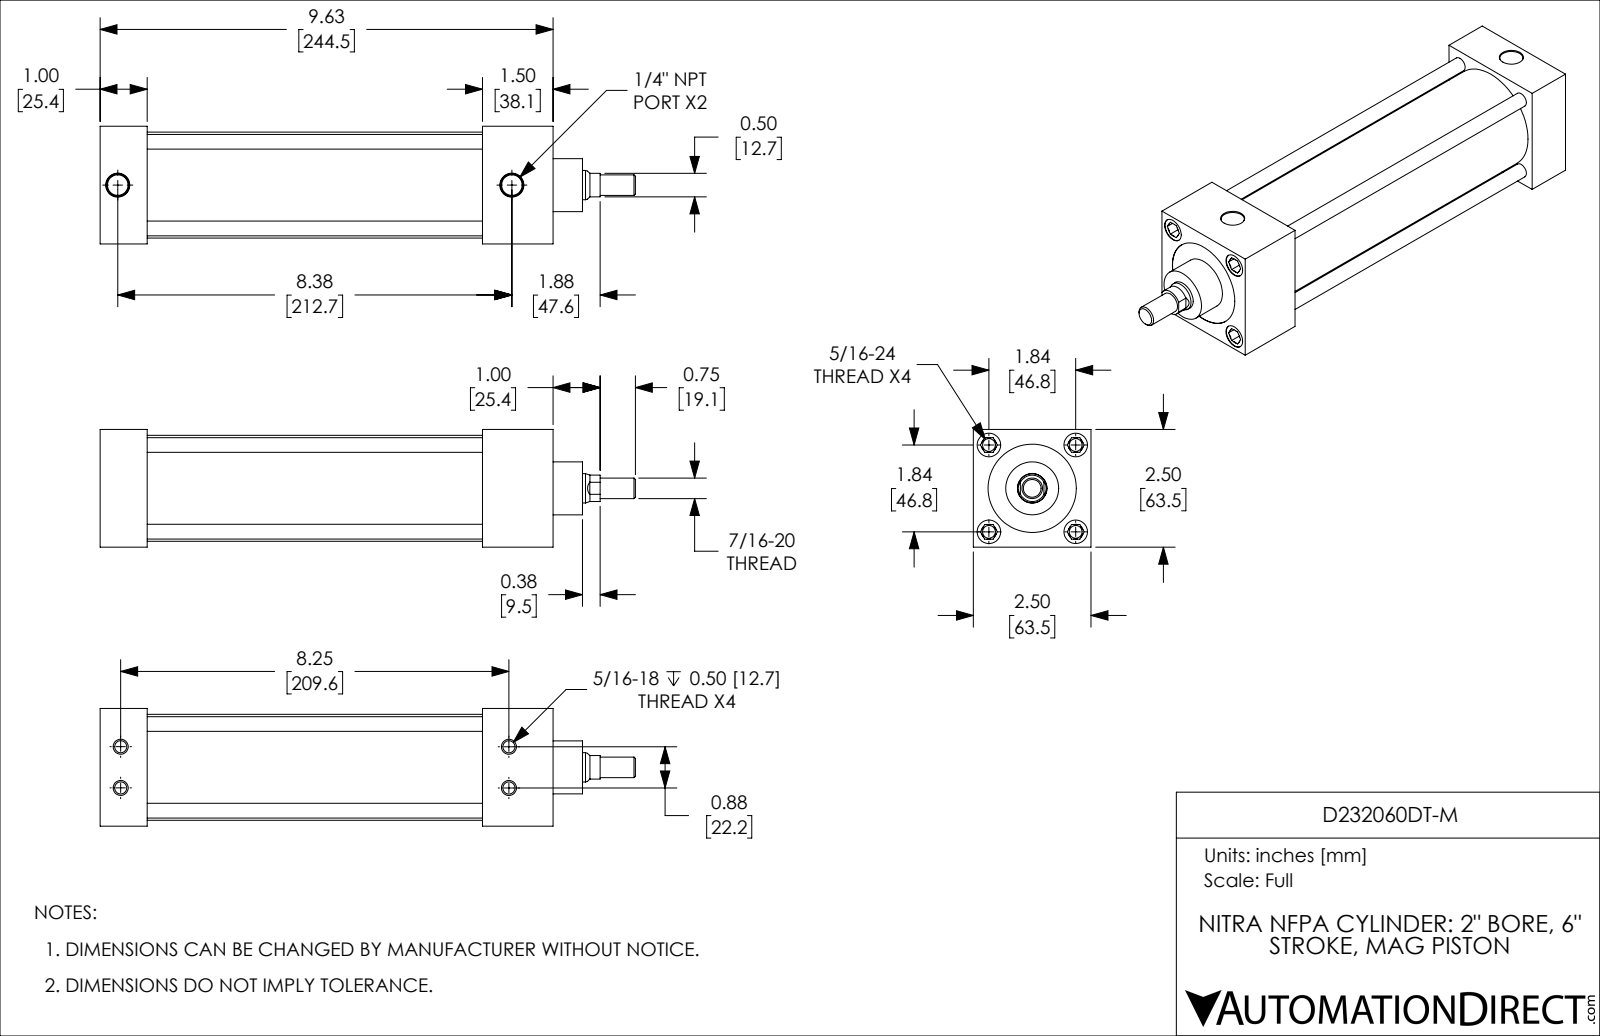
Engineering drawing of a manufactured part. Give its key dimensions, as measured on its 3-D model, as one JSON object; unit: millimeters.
{"part_name": "D232060DT-M_BODY; D232060DT-M_PISTON_KK1; D232060DT-M", "step_written_by": "SolidWorks 2019 (CONFIG_CONTROL_DESIGN)", "units": "millimeters", "bodies": {"solids": 2, "faces": 200, "planar": 58, "cylindrical": 62, "other": 80}, "overall_size": [288.9, 63.5, 63.5], "volume_mm3": 477400, "surface_area_mm2": 140200, "round_holes": [[6.9, 7], [6.5, 4], [12.7, 4], [11.1, 2], [15.9, 1], [47.6, 1], [50.8, 1]], "round_bosses_or_shafts": [[7.9, 4], [57.2, 1], [50.8, 1], [28.6, 1], [15.8, 1], [11.1, 1]], "partial_cylinders_radius": [[7.1, 1]], "face_to_face_distances": [63.5, 25.4, 206.4, 181, 54, 28.6, 152.4, 244.5, 219.1, 190.5], "hole_center_spacings": [46.7, 46.8, 33, 11.2, 11.3, 22.2, 33.1, 66.1]}
